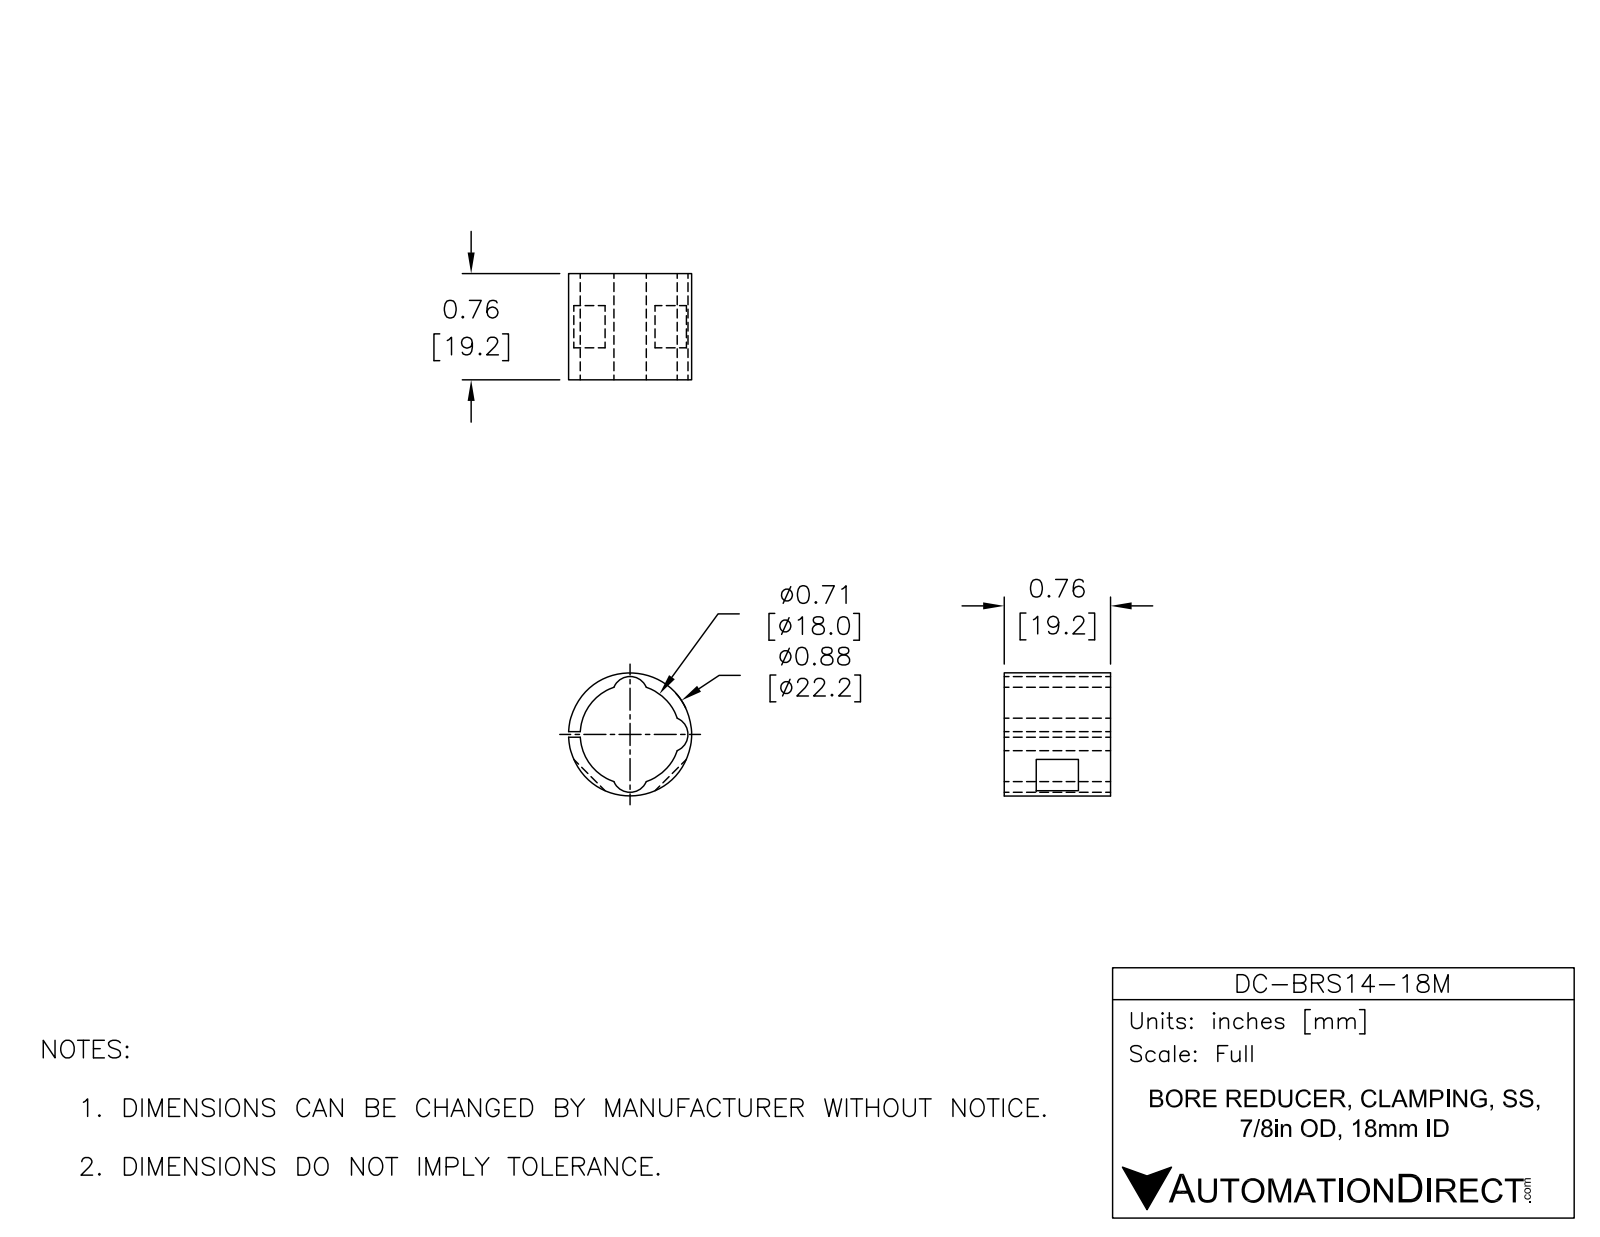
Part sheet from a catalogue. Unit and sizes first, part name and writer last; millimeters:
Units: millimetres
Overall size (bounding box): 22.23 × 22.21 × 19.18
Round bosses / shafts (diameter × count): ⌀22.22 ×1
Partial cylindrical surfaces — rounded edges, fillets, slot ends (radius × count): R3.17 ×3, R9 ×1
Main face-to-face distances: 19.18, 1.02, 5.78, 13.4, 7.62
Volume: 2 098 mm³ · Surface area: 2 789 mm²
Bodies: 1 solid, 21 faces (10 planar, 11 cylindrical, 0 other)
Part name (STEP PRODUCT): DC-BRS14-18M
STEP written by: SolidWorks 2015 (AUTOMOTIVE_DESIGN)
